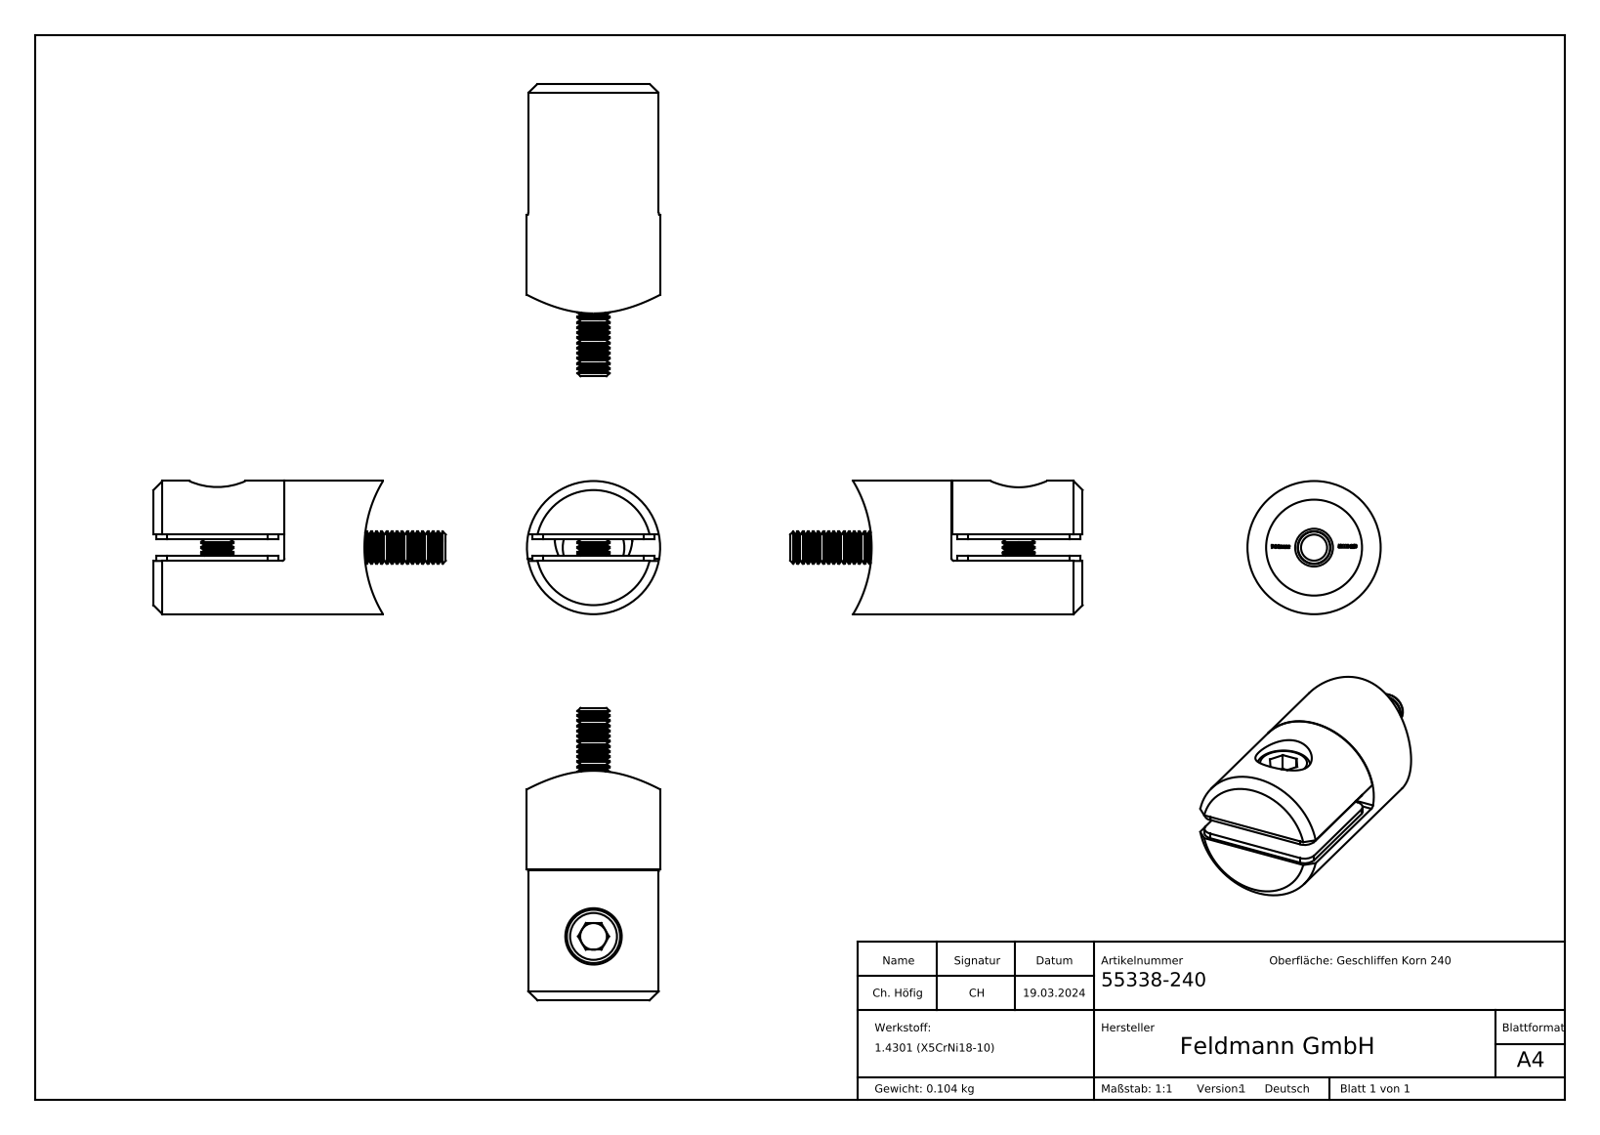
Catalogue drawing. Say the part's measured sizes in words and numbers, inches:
The part is named "5533X-240 Teil2_5533X-240 Teil2; socket head cap screw_din_DIN 912 M6 x 12 --- 12S; socket countersunk head screw_din_DIN 7991 - M6 x 25 --- 25S; 55338-240 (+2 more)". Its 3-D file was written by "SolidWorks 2018 (CONFIG_CONTROL_DESIGN)". It is 6 solids with 721 faces: 211 planar, 187 cylindrical and 323 other. Overall it measures 2.161 by 0.984 by 0.984 inches. Its volume is 0.939 cubic inches and its surface area 16.31 square inches. Round holes: 2 of diameter 0.157, 1 of diameter 0.197, 1 of diameter 0.256, 1 of diameter 0.276, 1 of diameter 0.28, 1 of diameter 0.417, 1 of diameter 0.575, 1 of diameter 0.709. Round bosses or shafts: 2 of diameter 0.236, 1 of diameter 0.984, 1 of diameter 0.456, 1 of diameter 0.394. Partial cylindrical surfaces (rounded edges, fillets, slot ends): 40 of radius 0.008, 6 of radius 0.079, 2 of radius 0.049, 1 of radius 0.02, 1 of radius 0.951. The main face-to-face distances are 0.157, 0.039, 0.197, 0.118, 1.358, 0.394, 0.965, 0.236, 0.39, 0.969. The hole center spacings are 0.369, 0.472.
